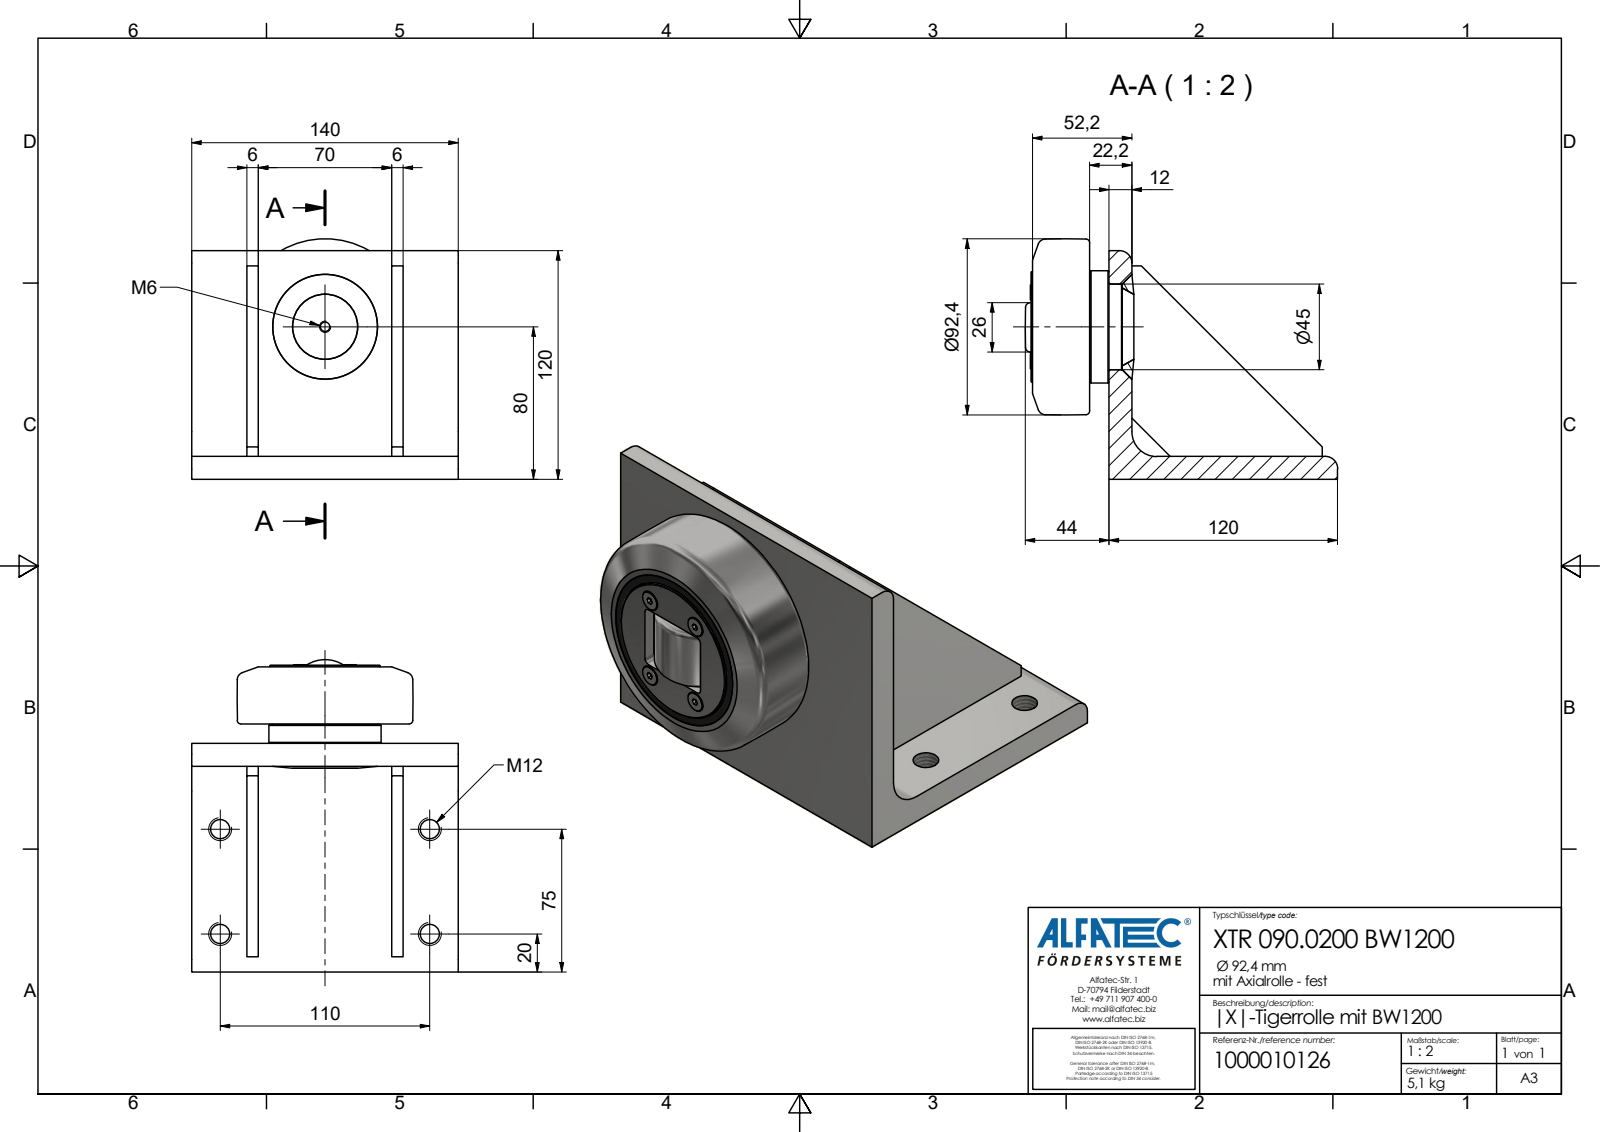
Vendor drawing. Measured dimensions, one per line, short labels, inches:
name: XTR 090.0200 BW1200_Kontur
written by: Autodesk Inventor 2020 (AP242_MANAGED_MODEL_BASED_3D_ENGINEERING_MIM_LF)
unit: in
bodies: 1 solid, 104 faces (67 planar, 22 cylindrical, 15 other)
size: 6.457 × 5.512 × 4.969
volume: 40.96 in³; area: 173.4 in²
holes: 4× ⌀0.398, 1× ⌀0.098, 1× ⌀0.194
bosses: 4× ⌀0.307, 1× ⌀2.323, 1× ⌀2.283, 1× ⌀2.177
rounds: 4× R0.079, 2× R0.256, 1× R0.059, 1× R0.512, 1× R0.984
face distances: 0.472, 2.992, 0.236, 1.142, 1.378, 4.134, 4.37, 3.228, 2.756, 0.402
hole spacings: 2.165, 4.331, 4.842
